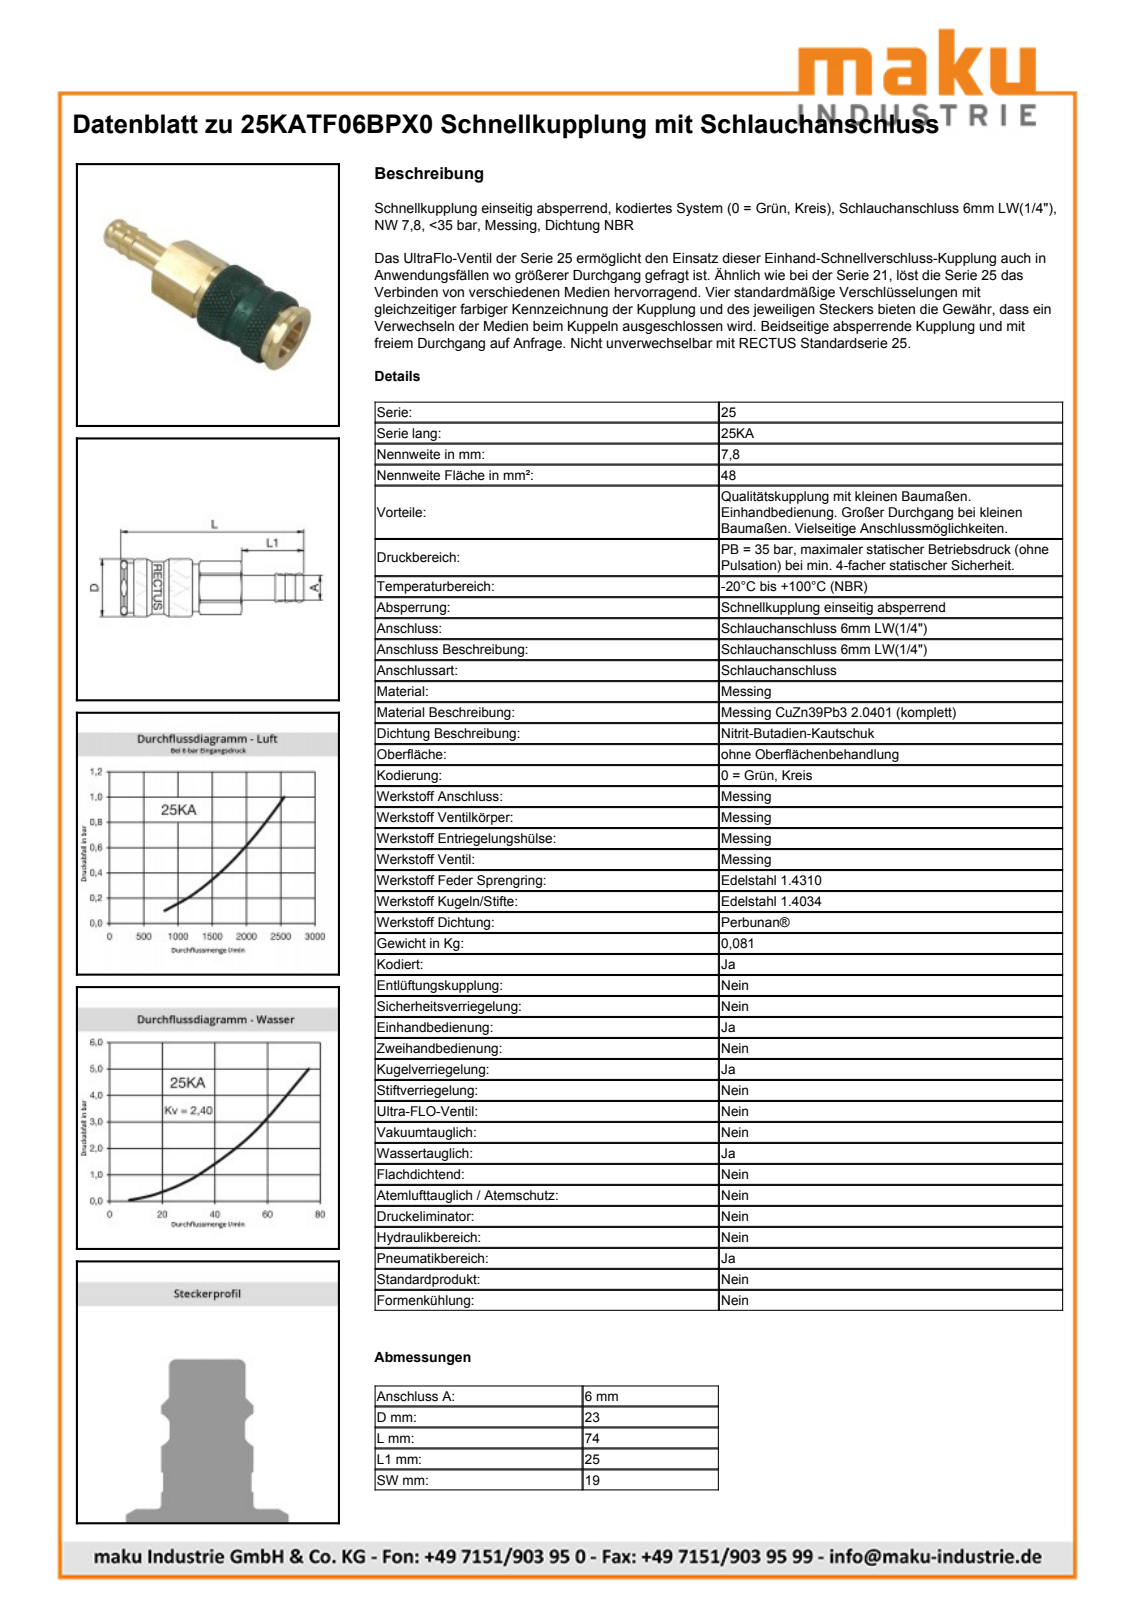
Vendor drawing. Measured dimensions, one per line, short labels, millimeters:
name: D113166
written by: Autodesk Inventor 2013 (AUTOMOTIVE_DESIGN)
unit: mm
bodies: 2 solids, 517 faces (195 planar, 64 cylindrical, 258 other)
size: 70.55 × 23.15 × 23.15
volume: 16 137 mm³; area: 7 512 mm²
holes: 1× ⌀14, 1× ⌀17.25, 1× ⌀19.35, 1× ⌀20.05
bosses: 1× ⌀23.15, 1× ⌀21, 1× ⌀20, 1× ⌀18.95, 1× ⌀16, 1× ⌀6.1
rounds: 1× R10.4, 1× R10.7, 1× R11
face distances: 19, 45.55, 21.55, 24, 21, 28.5, 6.95, 17.05, 5, 16.55
